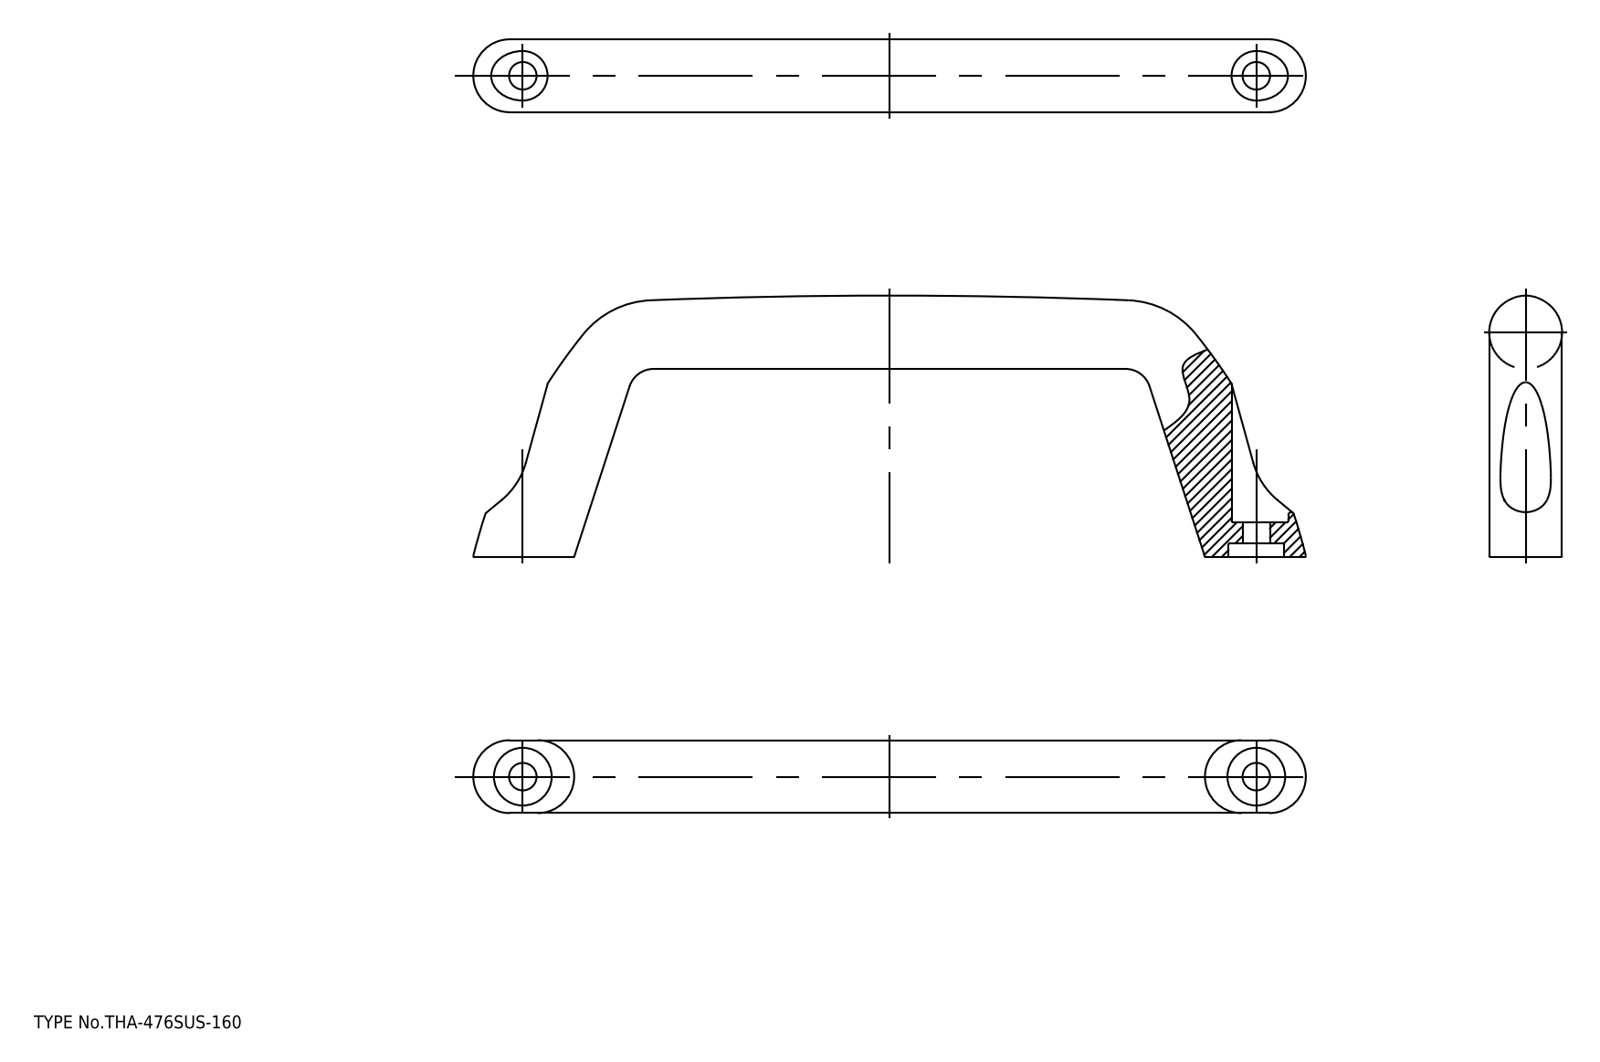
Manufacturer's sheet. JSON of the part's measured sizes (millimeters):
{"step_written_by": "spGate 20.6.3 (****-****-****-****) (AUTOMOTIVE_DESIGN)", "units": "millimeters", "bodies": {"solids": 1, "faces": 52, "planar": 6, "cylindrical": 12, "other": 34}, "overall_size": [181.6, 57, 16.11], "volume_mm3": 43024, "surface_area_mm2": 13078, "round_holes": [[6, 2], [12.6, 2]], "partial_cylinders_radius": [[5.4, 2], [7.95, 1]], "face_to_face_distances": [3, 7.5, 4.5], "hole_center_spacings": [160]}
